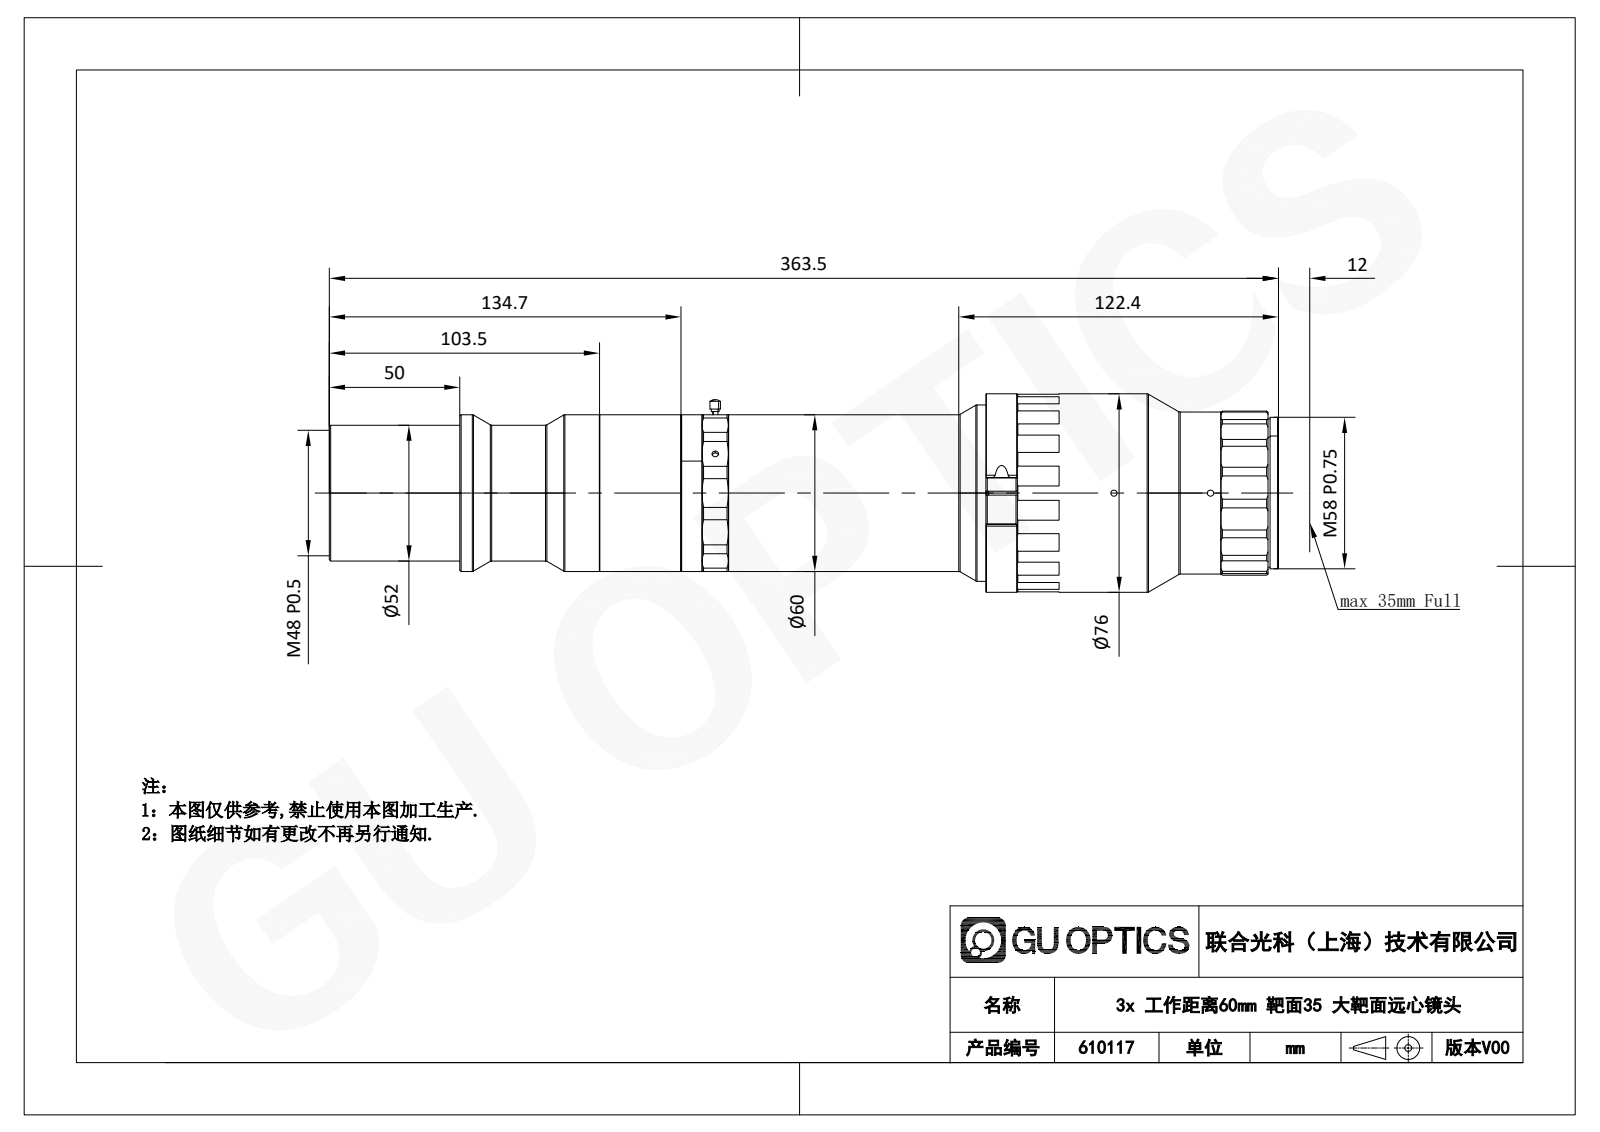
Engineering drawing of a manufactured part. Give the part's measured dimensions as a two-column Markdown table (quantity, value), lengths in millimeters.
| quantity | value |
| --- | --- |
| part name | DTCA35F-14.6-G-M58-AL |
| STEP written by | SolidWorks 2017 (CONFIG_CONTROL_DESIGN) |
| units | millimeters |
| bodies | 1 solid, 499 faces (133 planar, 170 cylindrical, 196 other) |
| overall size | 363.45 × 82.49 × 76 |
| volume | 1 017 000 mm³ |
| surface area | 90 686 mm² |
| round holes (diameter × count) | 2.4 × 6, 2.5 × 3, 2.2 × 1, 3.4 × 1, 4.5 × 1, 46.5 × 1, 47.5 × 1, 51.5 × 1, 55 × 1, 55.5 × 1, 72.3 × 1 |
| round bosses / shafts (diameter × count) | 76 × 1, 72 × 1, 71 × 1, 67.5 × 1, 62 × 1, 60 × 1, 58 × 1, 56.8 × 1 |
| partial cylindrical surfaces (radius × count) | 15 × 34, 1 × 2, 4 × 1, 30.5 × 1, 31.5 × 1, 44.5 × 1 |
| main face-to-face distances | 60, 201.45, 309.45, 108, 313.45, 112, 4, 283.45, 82, 26 |
| hole center spacings | 37, 116.89 |
